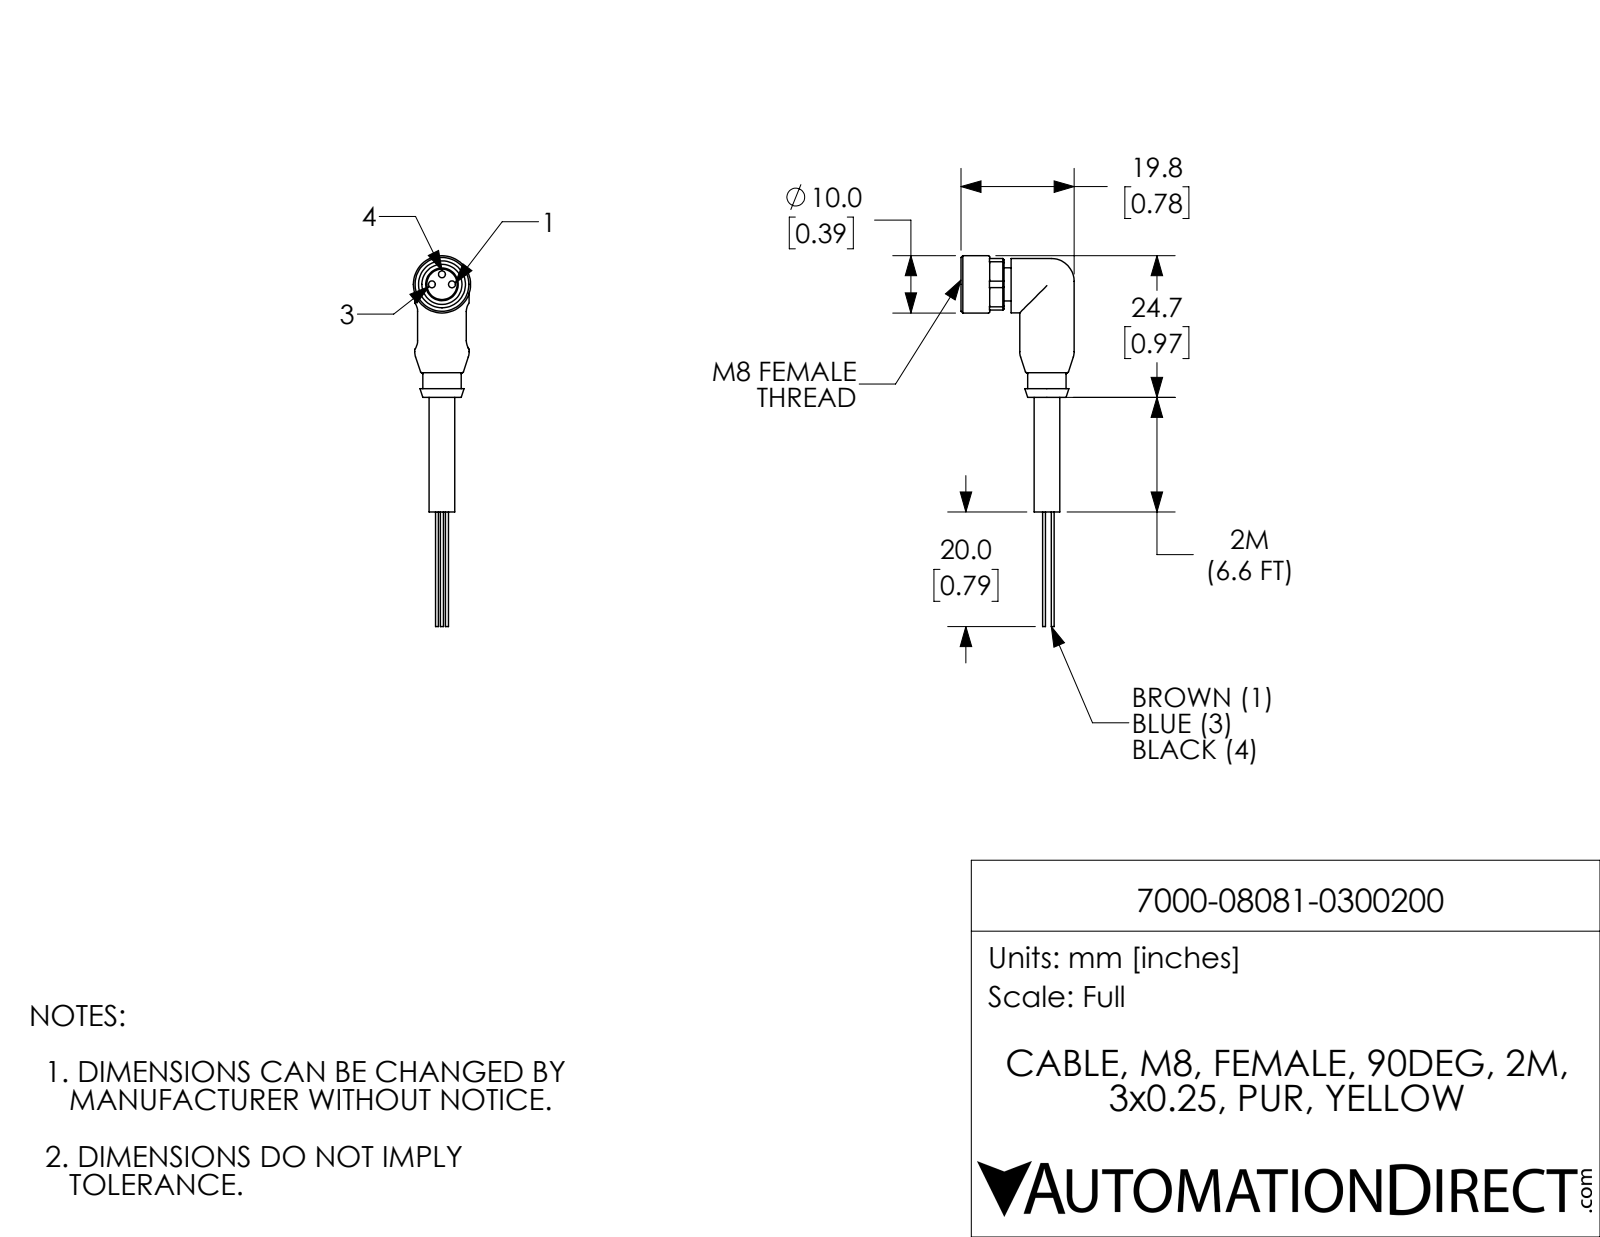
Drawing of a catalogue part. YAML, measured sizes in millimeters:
part_name: "7000-08081-0300200"
step_written_by: "SolidWorks 2021 (CONFIG_CONTROL_DESIGN)"
units: millimeters
bodies: {solids: 1, faces: 107, planar: 35, cylindrical: 43, other: 29}
overall_size: [64.7, 19.8, 10]
volume: 2410
surface_area: 1835
round_holes:
  - {diameter: 1.2, count: 3}
  - {diameter: 7, count: 1}
round_bosses_or_shafts:
  - {diameter: 0.5, count: 3}
  - {diameter: 9.5, count: 2}
  - {diameter: 10, count: 1}
  - {diameter: 6.7, count: 1}
  - {diameter: 5.8, count: 1}
  - {diameter: 5.7, count: 1}
  - {diameter: 4.5, count: 1}
partial_cylinders:
  - {radius: 0.2, count: 4}
  - {radius: 2.5, count: 4}
  - {radius: 4.9, count: 1}
face_to_face_distances: [1.2, 9, 1.5, 8.5, 0.7, 6.8, 8.1, 7.5, 8.7, 20]
hole_center_spacings: [1.8, 2.5, 3.5]
